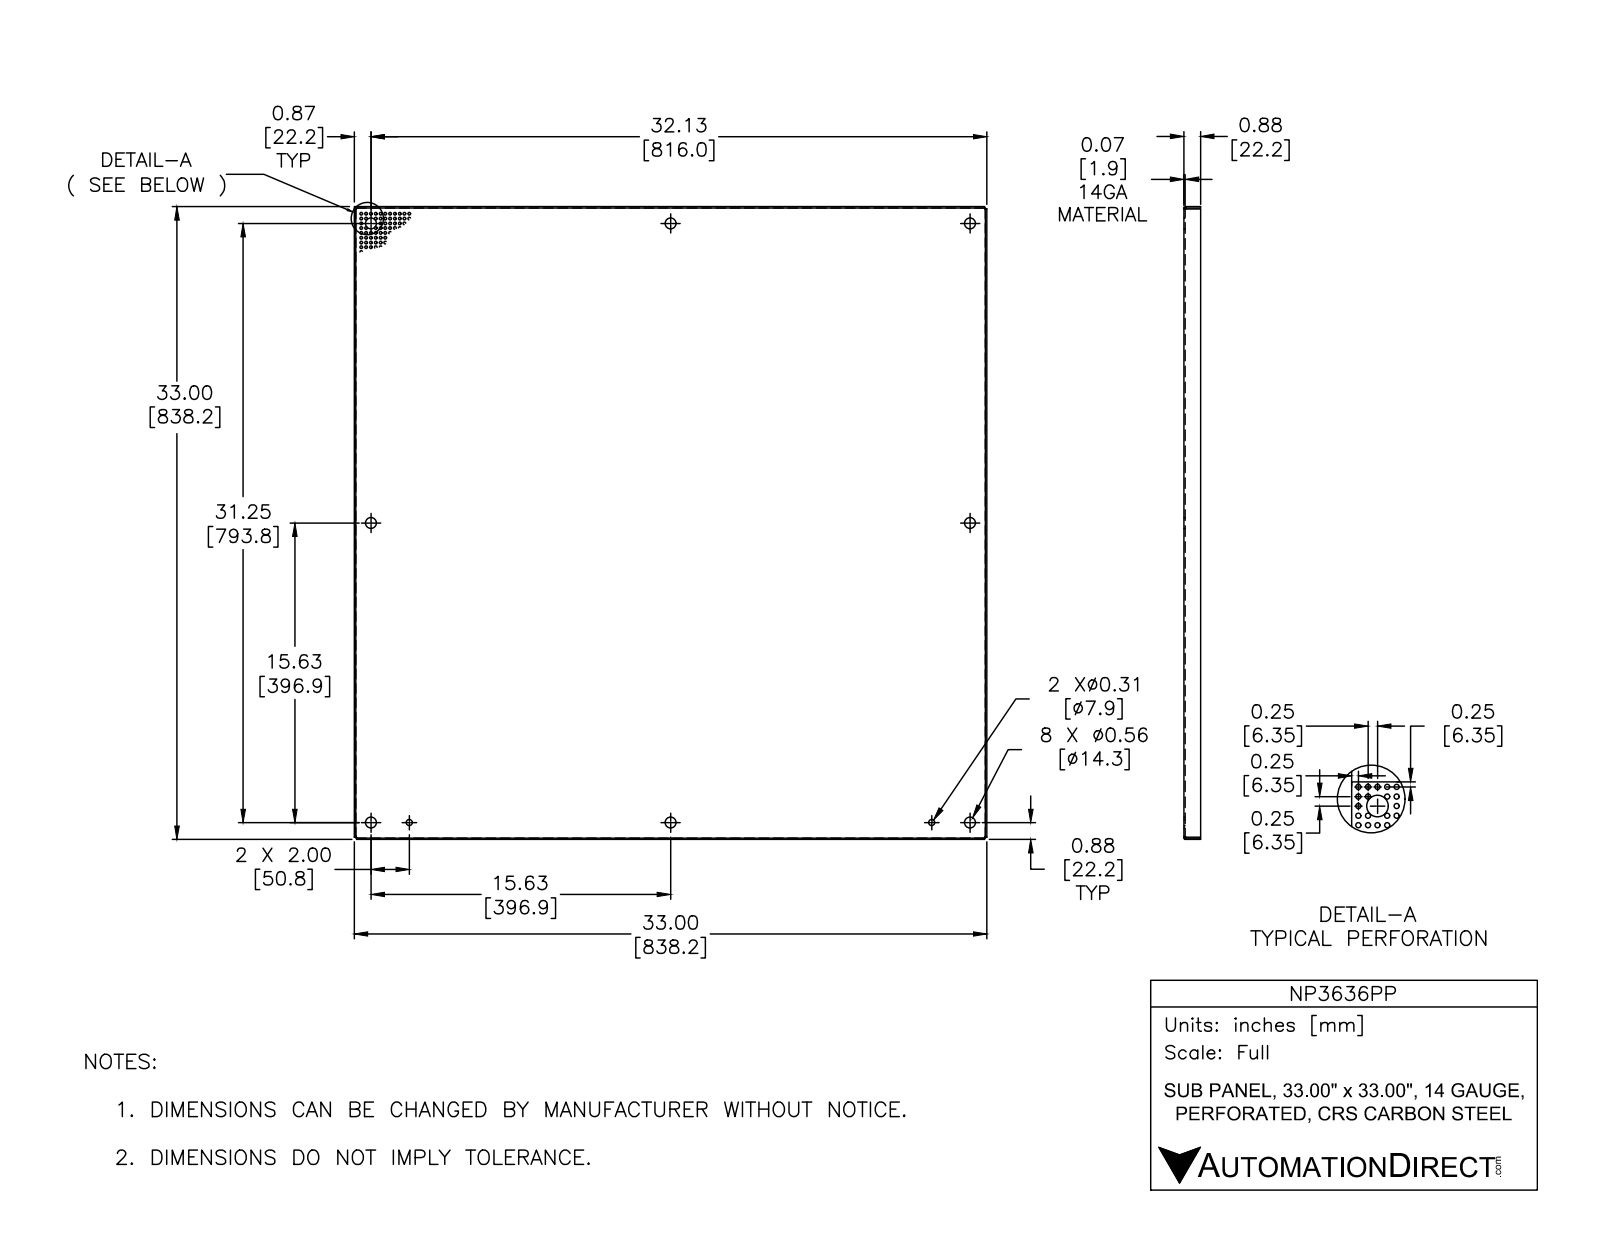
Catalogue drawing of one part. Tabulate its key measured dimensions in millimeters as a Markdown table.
| quantity | value |
| --- | --- |
| part name | NP3636PP |
| STEP written by | Autodesk Inventor 2012 (AUTOMOTIVE_DESIGN) |
| units | millimeters |
| bodies | 1 solid, 48 faces (22 planar, 18 cylindrical, 8 other) |
| overall size | 838.2 × 838.2 × 22.2 |
| volume | 1 440 000 mm³ |
| surface area | 1 540 000 mm² |
| round holes (diameter × count) | 14.3 × 8, 7.9 × 2 |
| partial cylindrical surfaces (radius × count) | 0.8 × 4, 2.7 × 4 |
| main face-to-face distances | 1.9, 836.3, 838.2, 834.4, 20.3, 22.2, 3.2, 835, 1.3, 833.1 |
| hole center spacings | 887.5, 793.8, 396.9, 396.9, 561.3, 400.1, 795.4, 887.5 |
